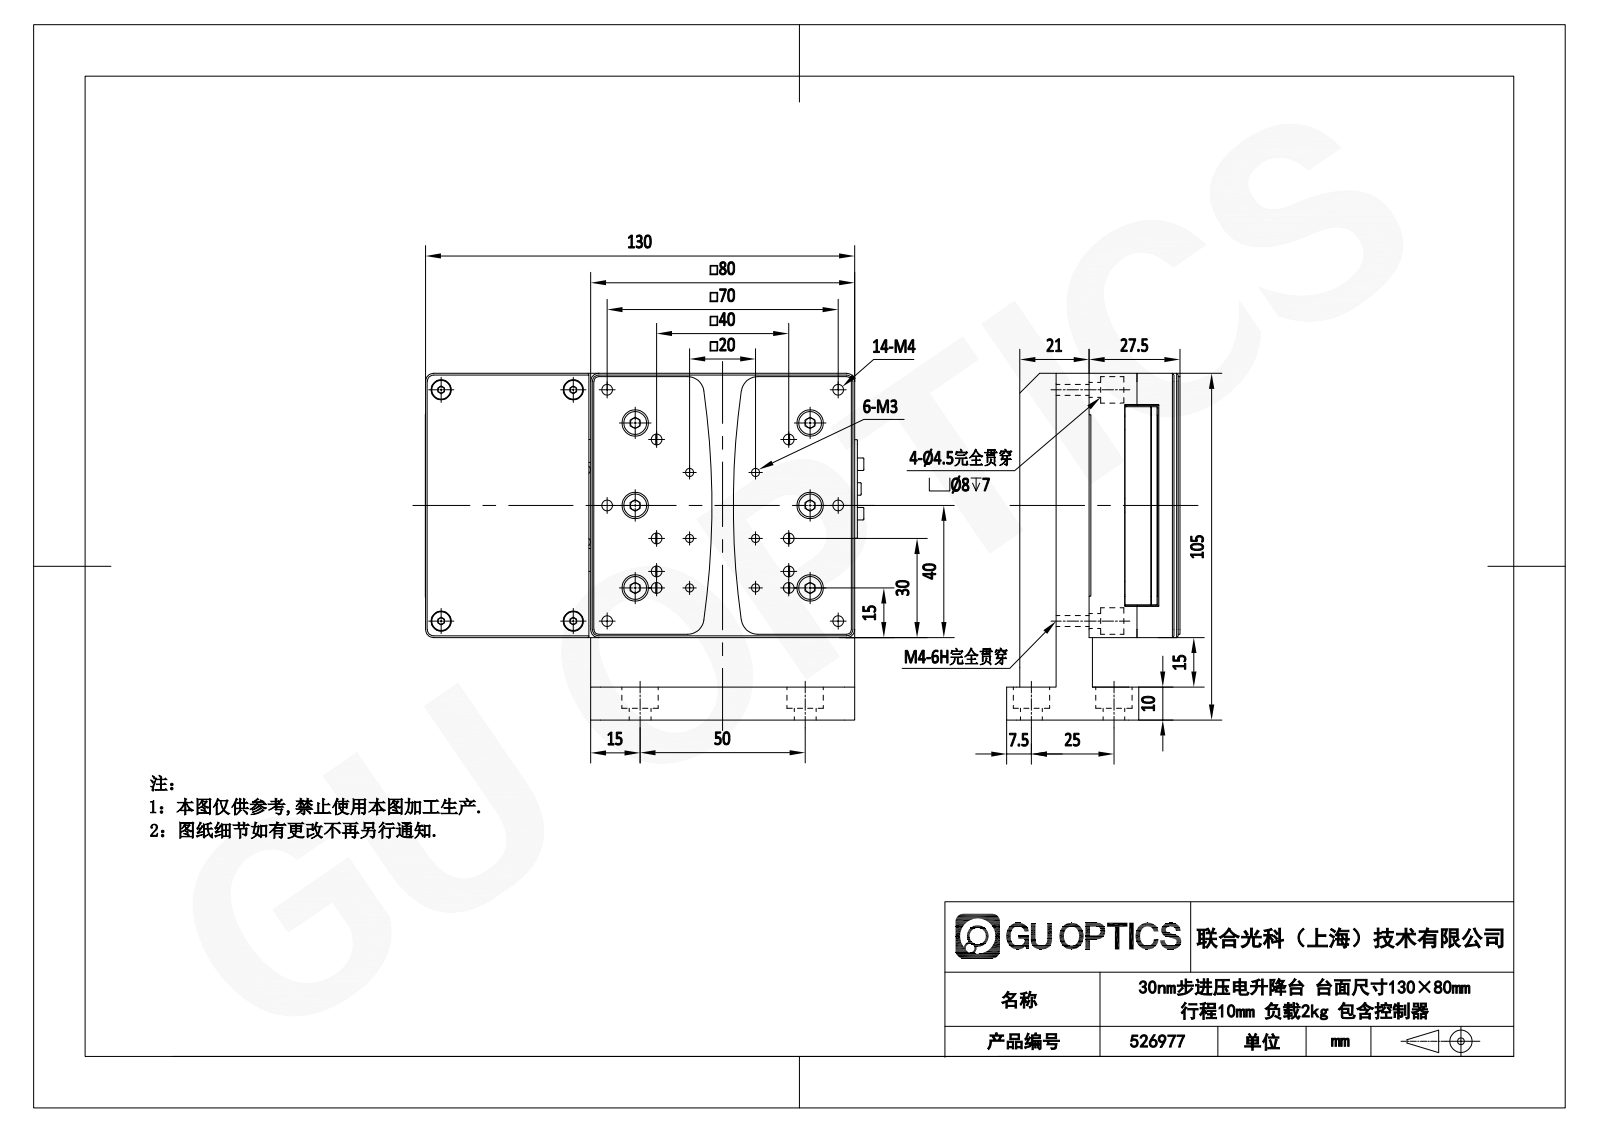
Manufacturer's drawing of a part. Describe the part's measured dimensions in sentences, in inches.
The part is named "526962". Its 3-D file was written by "SolidWorks 2020 (CONFIG_CONTROL_DESIGN)". It is 41 solids with 1845 faces: 904 planar, 628 cylindrical and 313 other. Overall it measures 5.23 by 4.134 by 2.067 inches. Its volume is 22.91 cubic inches and its surface area 193 square inches. Round holes: 20 of diameter 0.098, 18 of diameter 0.13, 16 of diameter 0.134, 16 of diameter 0.177, 16 of diameter 0.315, 15 of diameter 0.236, 7 of diameter 0.063, 7 of diameter 0.118, 4 of diameter 0.049, 4 of diameter 0.081, 4 of diameter 0.122, 4 of diameter 0.213. Round bosses or shafts: 12 of diameter 0.276, 12 of diameter 0.157, 12 of diameter 0.016, 6 of diameter 0.224, 6 of diameter 0.118, 4 of diameter 0.272, 4 of diameter 0.197, 4 of diameter 0.098. Partial cylindrical surfaces (rounded edges, fillets, slot ends): 38 of radius 0.059, 16 of radius 0.079, 12 of radius 0.039, 11 of radius 0.02, 10 of radius 0.118, 8 of radius 0.098, 6 of radius 0.008, 4 of radius 0.075. The main face-to-face distances are 0.02, 0.394, 0.413, 0.335, 0.433, 0.315, 0.748, 0.827, 0.406, 1.063. The hole center spacings are 0.984, 1.969, 0.256, 2.756, 0.313, 0.863, 1.158, 1.568.
